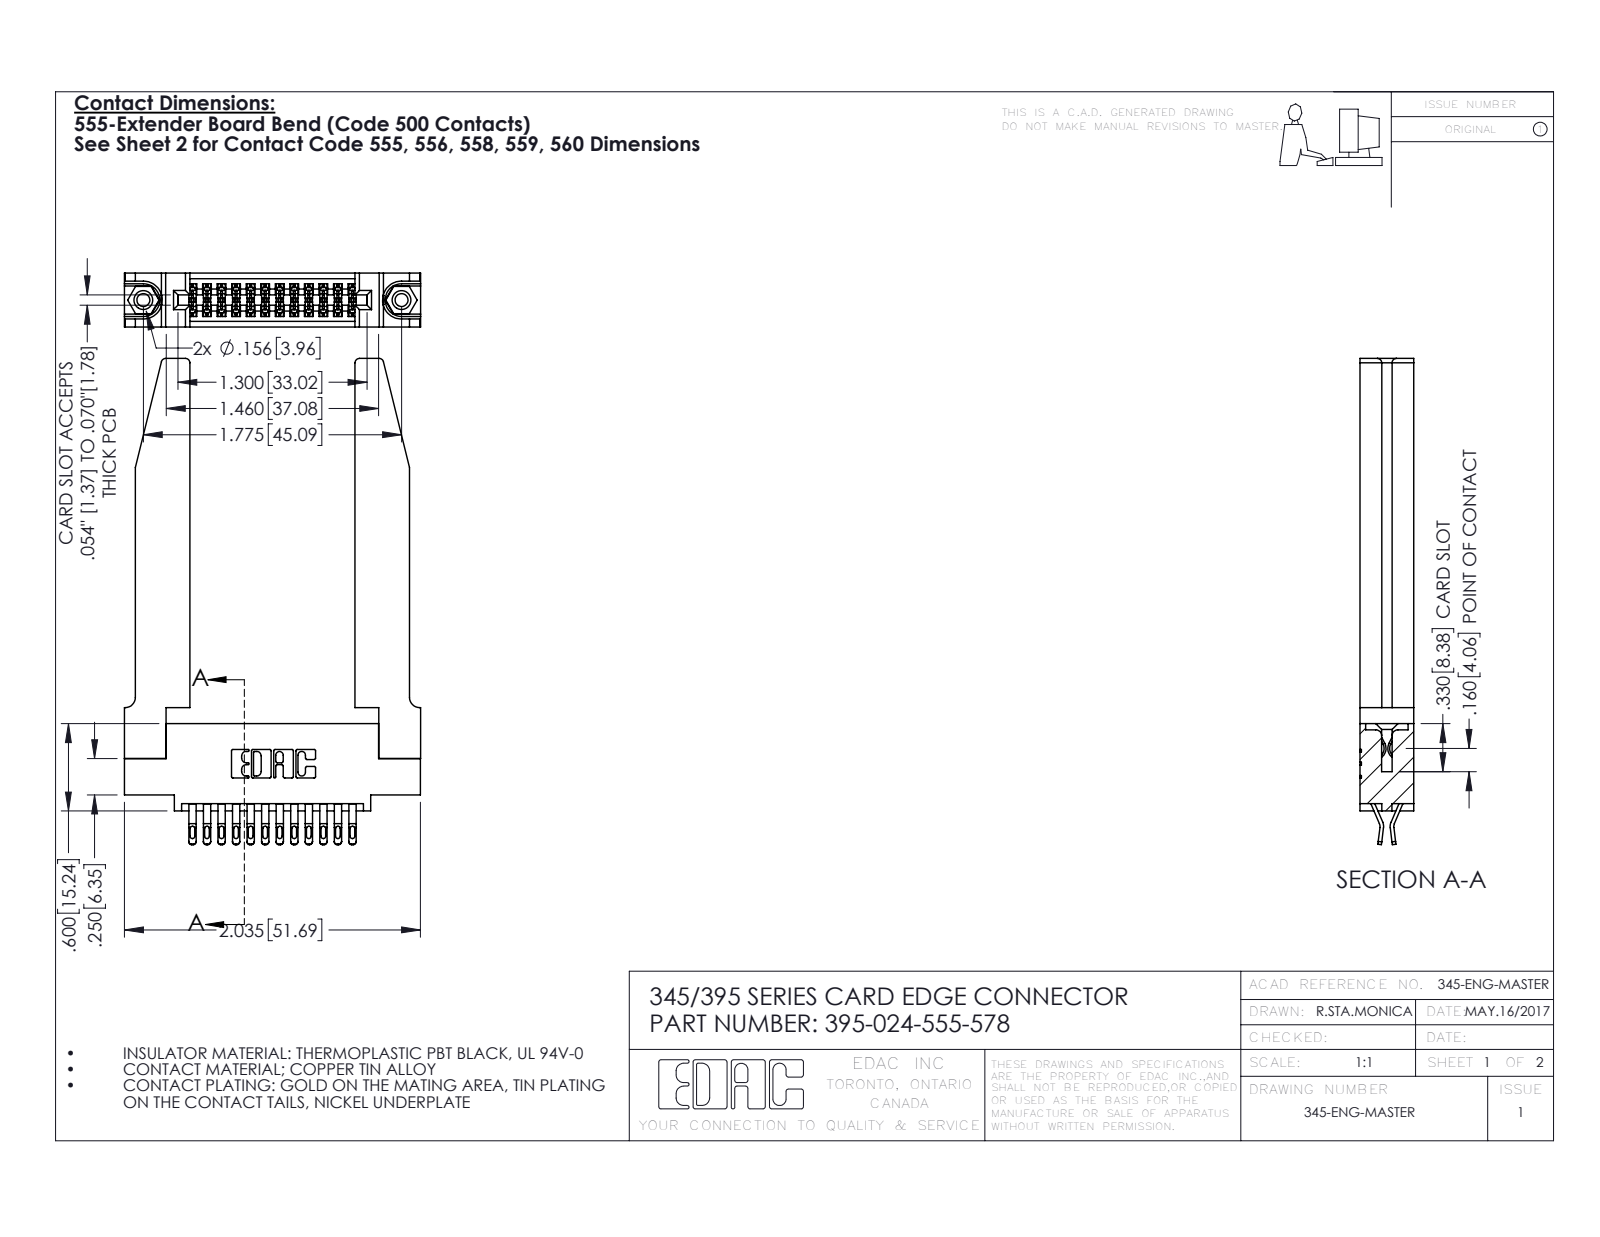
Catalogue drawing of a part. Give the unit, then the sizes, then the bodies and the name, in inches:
Units: inches
Overall size (bounding box): 3.342 × 2.036 × 0.37
Round holes (diameter × count): ⌀0.089 ×2, ⌀0.125 ×2, ⌀0.156 ×2, ⌀0.064 ×1
Round bosses / shafts (diameter × count): ⌀0.155 ×2
Partial cylindrical surfaces — rounded edges, fillets, slot ends (radius × count): R0.016 ×60, R0.02 ×48, R0.006 ×36, R0.01 ×22, R0.03 ×8, R0.007 ×6, R0.031 ×6, R0.026 ×3
Main face-to-face distances: 0.37, 0.072, 0.298, 0.15, 0.148, 0.22, 0.077, 0.025, 1.135, 0.2
Hole centre spacings: 0.27, 1.543, 1.775
Volume: 0.764 in³ · Surface area: 21.08 in²
Bodies: 29 solids, 1708 faces (970 planar, 686 cylindrical, 52 other)
Part name (STEP PRODUCT): 345 Part_0.110 Offset - 0.156 Dia-TH; 345-292-001_555 Tail; 345-220-078_345-220-078; 345-250-001_345-250-001-102 (+1 more)
STEP written by: SolidWorks 2016 (CONFIG_CONTROL_DESIGN)
